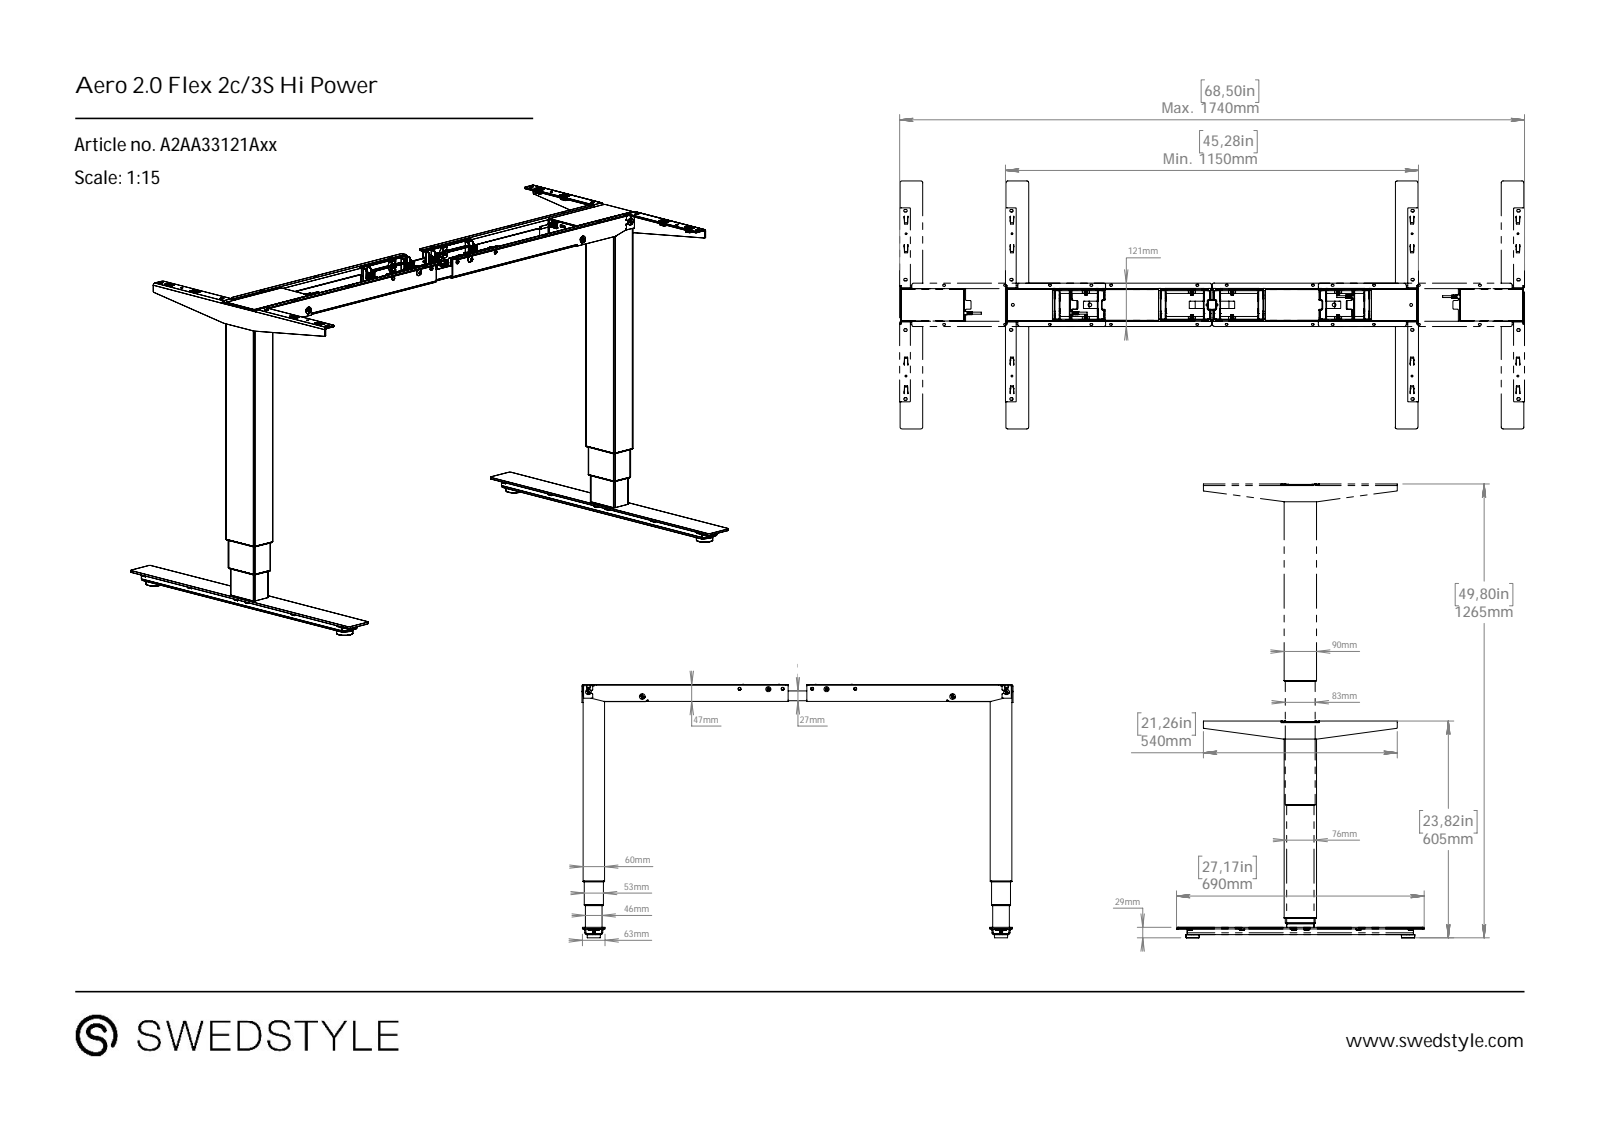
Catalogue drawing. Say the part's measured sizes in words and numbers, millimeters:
The part is named "A2AA33121Axx Aero 2.0 Flex 2c_3S Hi Power". Its 3-D file was written by "SolidWorks 2021 (CONFIG_CONTROL_DESIGN)". It is 0 solids with 1560 faces: 782 planar, 590 cylindrical and 188 other. Overall it measures 1200 by 705.5 by 690 millimeters. Round holes: 8 of diameter 16, 6 of diameter 8, 4 of diameter 5, 4 of diameter 14, 2 of diameter 10, 1 of diameter 5.4. Round bosses or shafts: 4 of diameter 15.57, 2 of diameter 14, 2 of diameter 8.5, 2 of diameter 8, 2 of diameter 7.6, 2 of diameter 5.5. Partial cylindrical surfaces (rounded edges, fillets, slot ends): 104 of radius 0.5, 72 of radius 2.5, 40 of radius 1, 24 of radius 2.75, 18 of radius 2, 18 of radius 3, 16 of radius 4, 14 of radius 5. The main face-to-face distances are 2, 1134, 3.5, 4, 6.9, 3.4, 2.5, 0.5, 56.5, 53.1. The hole center spacings are 203.3, 237.26, 1134, 22, 26.63, 33.62, 34, 40.5.
